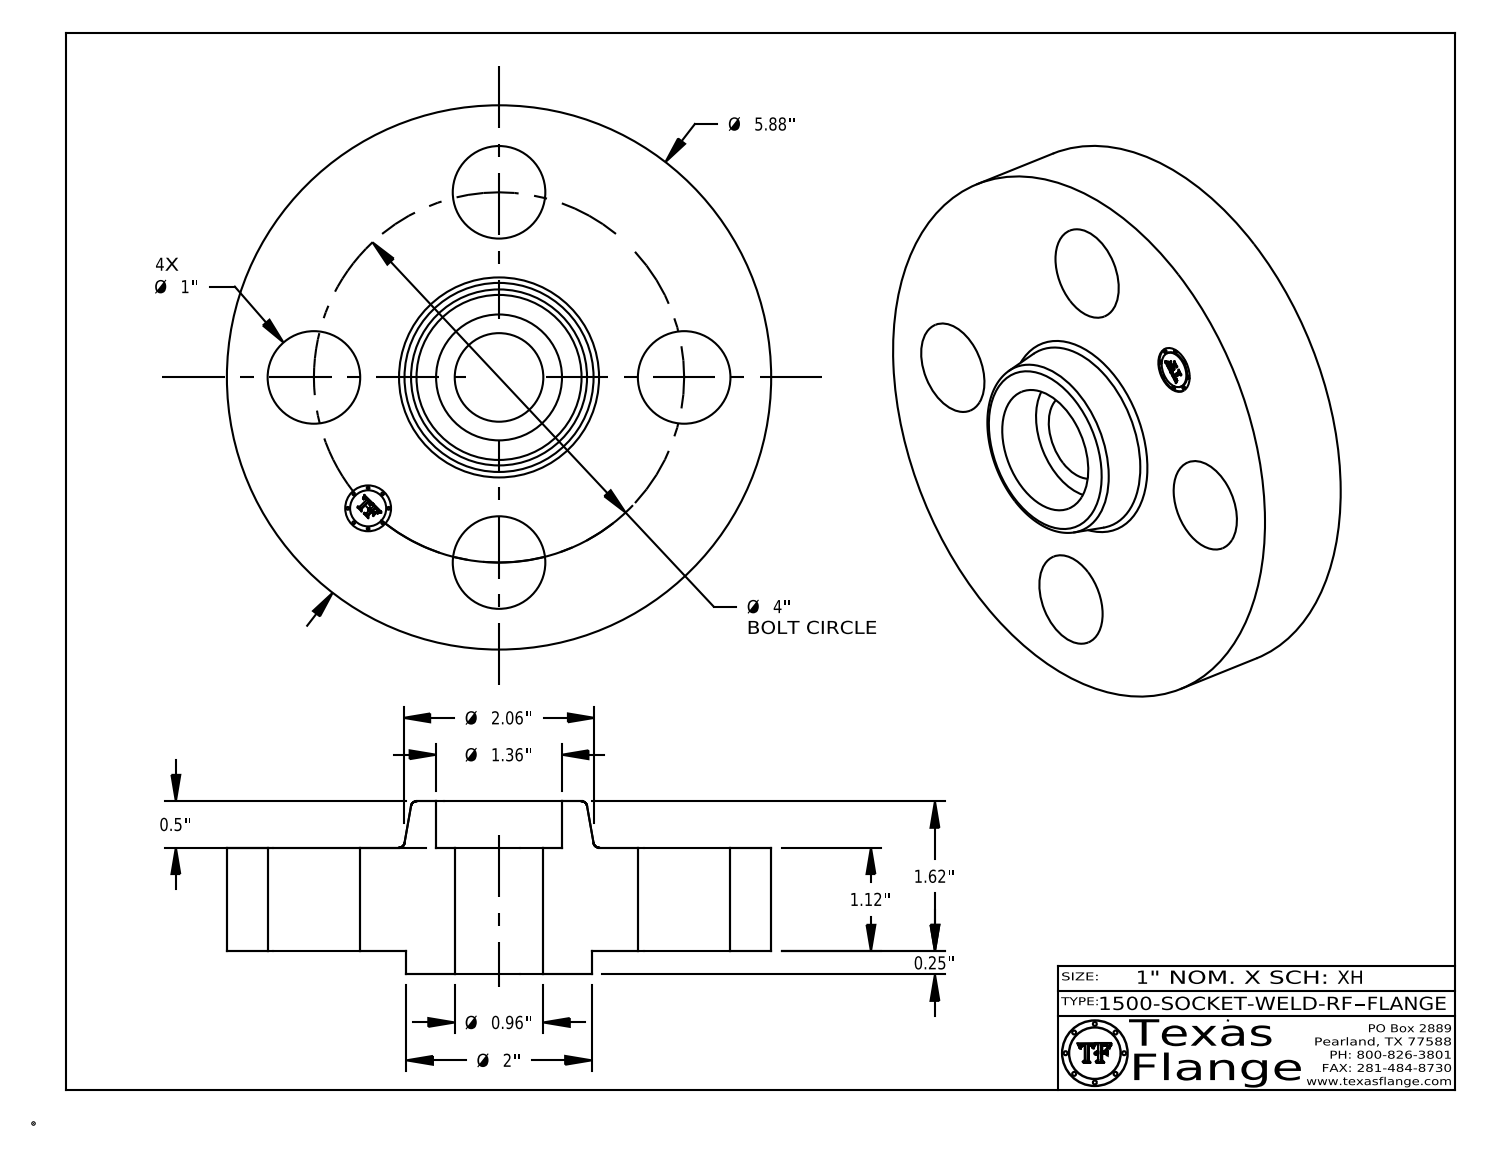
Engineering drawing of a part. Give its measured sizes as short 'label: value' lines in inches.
name: 1500-SOCKET-WELD-RF
written by: CATIA V5 STEP AP214 (AUTOMOTIVE_DESIGN)
unit: in
bodies: 1 solid, 412 faces (370 planar, 36 cylindrical, 6 other)
size: 5.88 × 5.88 × 1.87
volume: 27.5 in³; area: 91.66 in²
holes: 4× ⌀1, 1× ⌀0.495, 1× ⌀0.957, 1× ⌀1.36
bosses: 8× ⌀0.03, 1× ⌀5.88, 1× ⌀2, 1× ⌀0.39
face distances: 1.12, 0.25, 1.37, 1.87, 1.62, 0.5, 0.015, 1.355, 1.105, 0.515
hole spacings: 2, 2.828, 1.531, 3.695, 4
